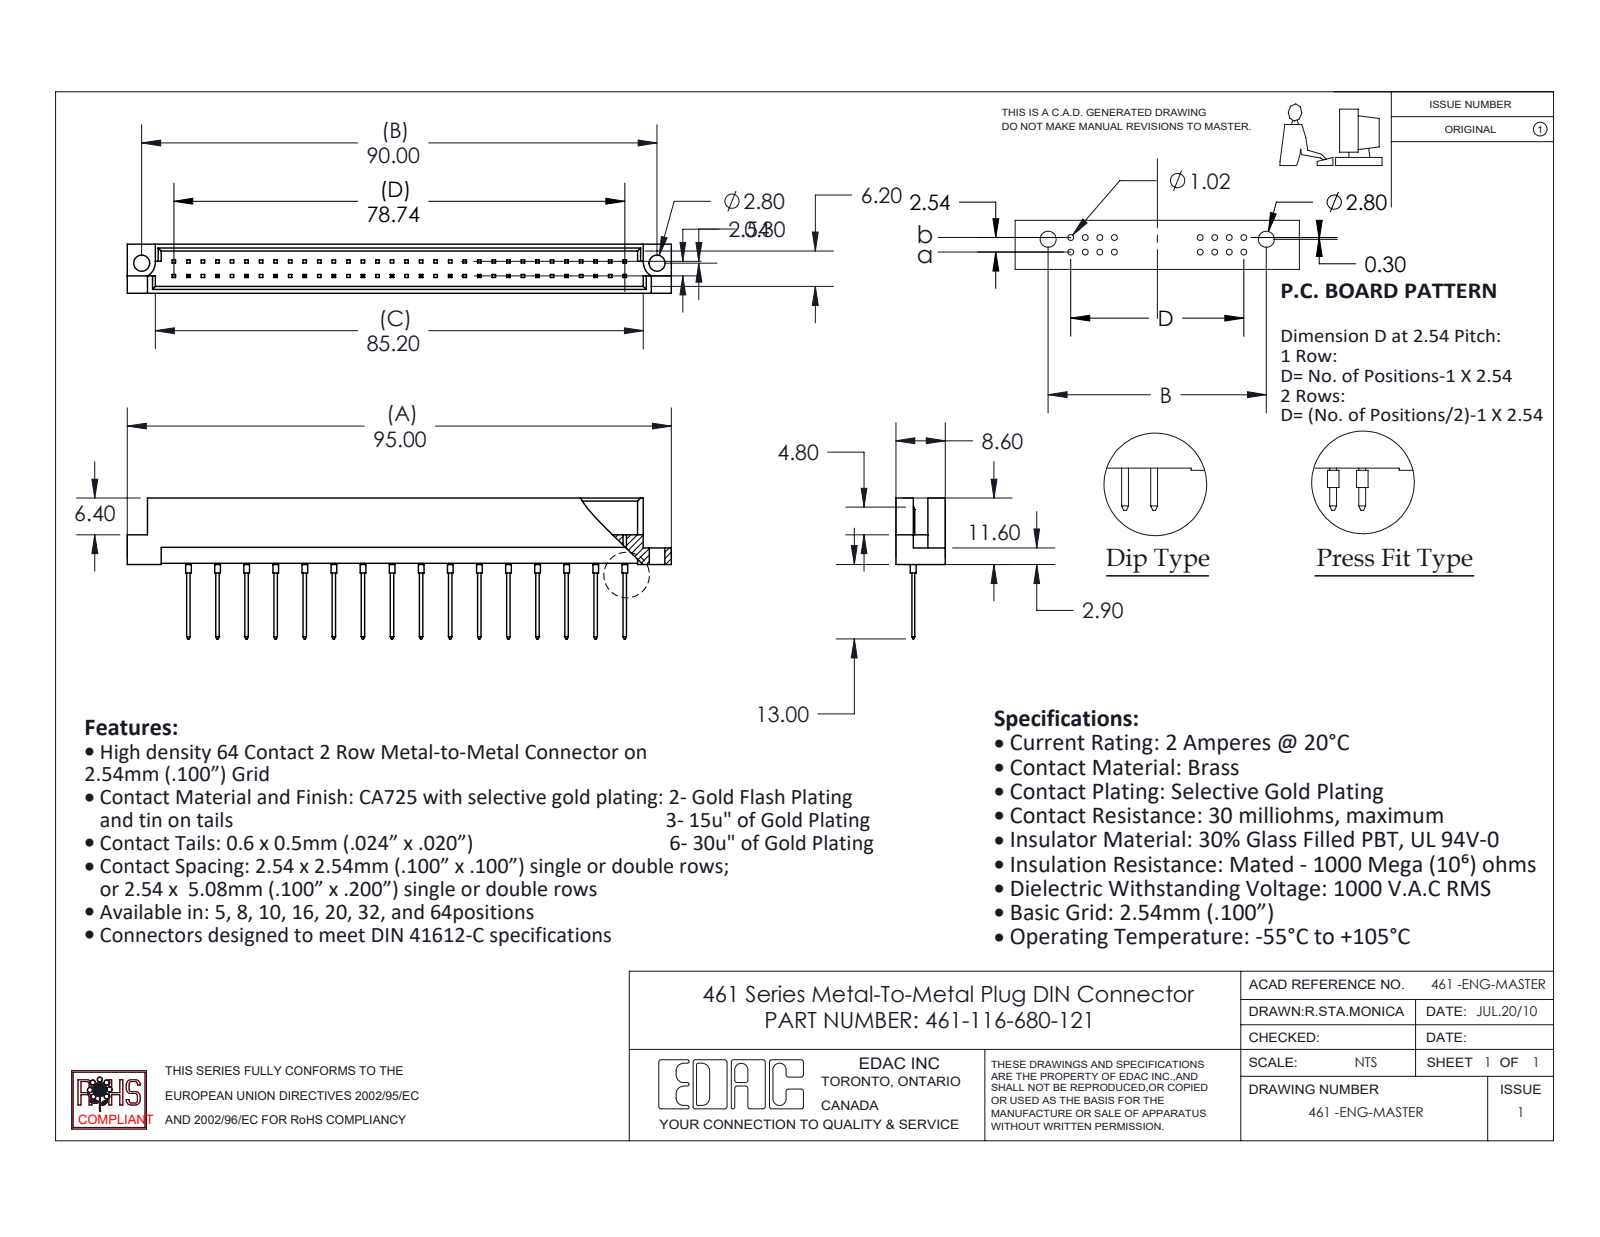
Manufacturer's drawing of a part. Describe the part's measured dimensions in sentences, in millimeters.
The part is named "461-116-680-121; 461 Part_64; 461-290_80". Its 3-D file was written by "SolidWorks 2020 (CONFIG_CONTROL_DESIGN)". It is 17 solids with 657 faces: 618 planar, 39 cylindrical and 0 other. Overall it measures 95 by 24.6 by 8.6 millimeters. Its volume is 4 777 cubic millimeters and its surface area 6 513 square millimeters. Round holes: 2 of diameter 2.8. Round bosses or shafts: 16 of diameter 1. Partial cylindrical surfaces (rounded edges, fillets, slot ends): 2 of radius 2.8. The main face-to-face distances are 1.2, 7.4, 8.6, 6.2, 5, 3.28, 5.32, 2.08, 4.12, 2.78. The hole center spacings are 90.
